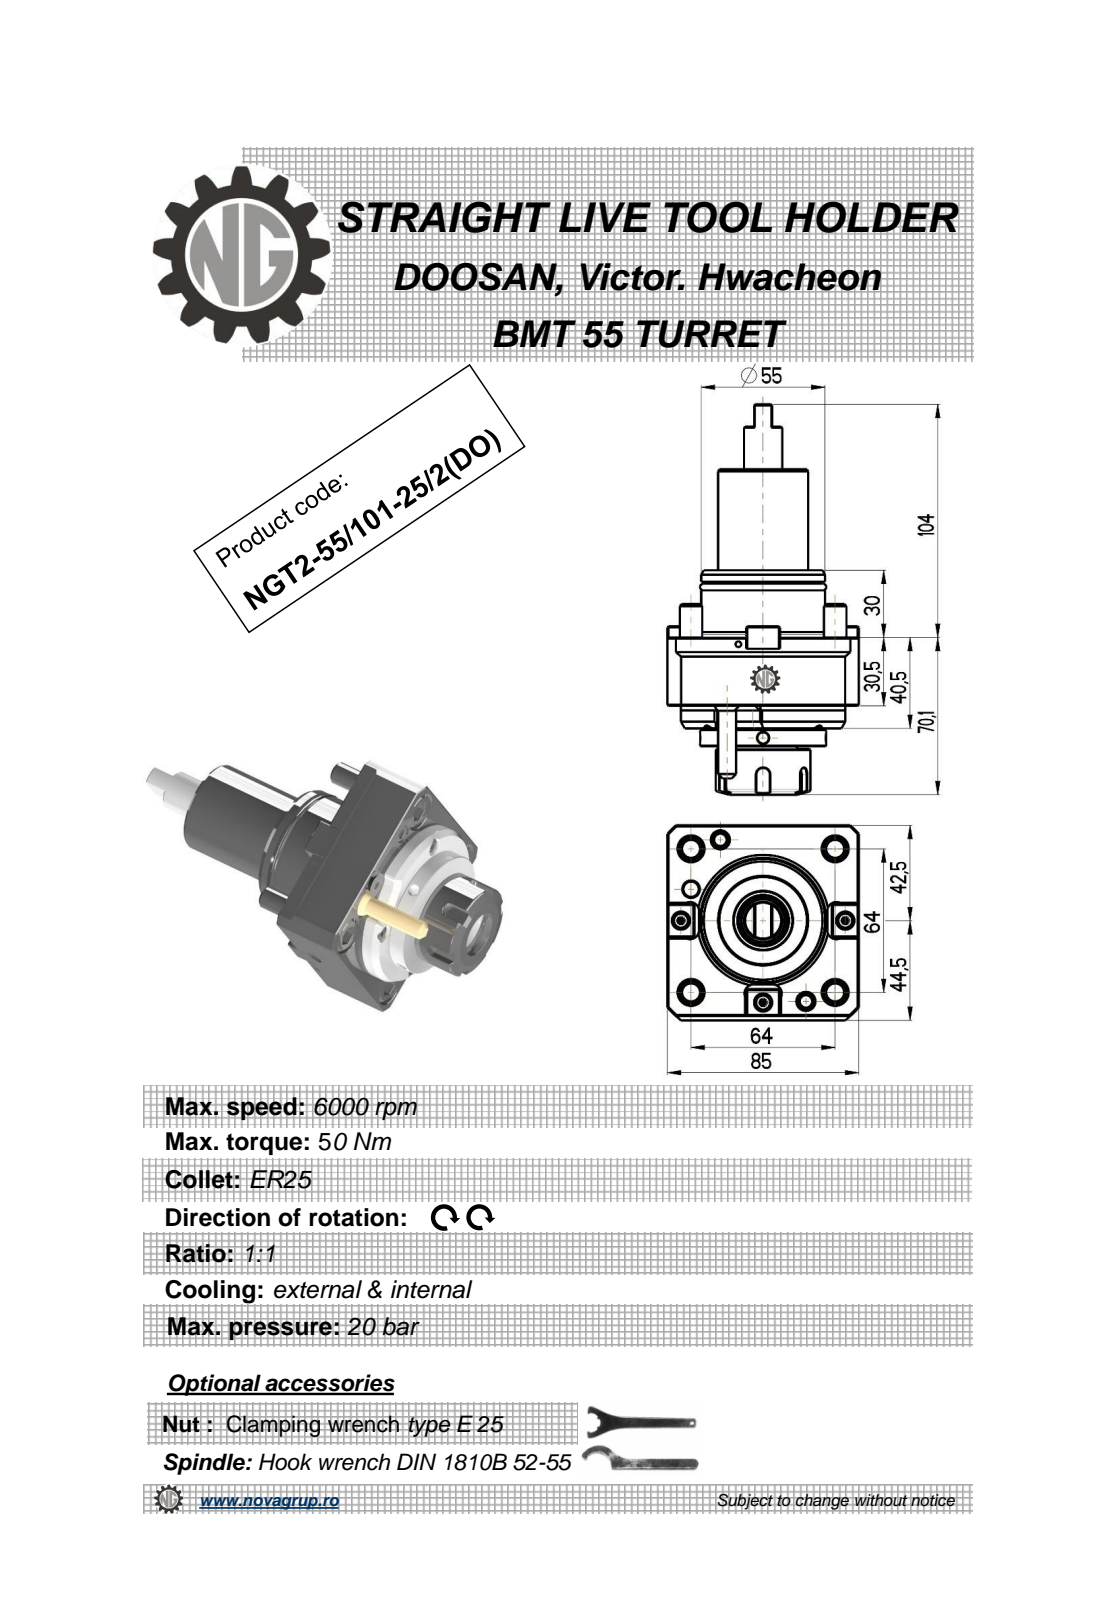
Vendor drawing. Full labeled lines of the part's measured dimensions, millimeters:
Part name (STEP PRODUCT): NGT2_55_101_25_1_DO
STEP written by: PRO/ENGINEER BY PARAMETRIC TECHNOLOGY CORPORATION, 2010280 (CONFIG_CONTROL_DESIGN)
Units: millimetres
Bodies: 2 solids, 318 faces (140 planar, 67 cylindrical, 111 other)
Overall size (bounding box): 174.1 × 88.6 × 85
Volume: 448 724 mm³ · Surface area: 53 500 mm²
Round holes (diameter × count): ⌀5 ×3, ⌀3 ×1, ⌀6.8 ×1, ⌀20.3 ×1
Round bosses / shafts (diameter × count): ⌀10 ×4, ⌀73 ×1, ⌀56 ×1, ⌀55 ×1, ⌀54.4 ×1, ⌀50 ×1, ⌀43 ×1, ⌀42 ×1
Partial cylindrical surfaces — rounded edges, fillets, slot ends (radius × count): R0.22 ×6, R3 ×5, R0.8 ×2, R6 ×2, R57.5 ×1
Main face-to-face distances: 30.5, 85, 10, 40.5, 8, 48.5, 87, 18, 10.5, 60.5
Hole centre spacings: 34.93, 37.12, 50.12
